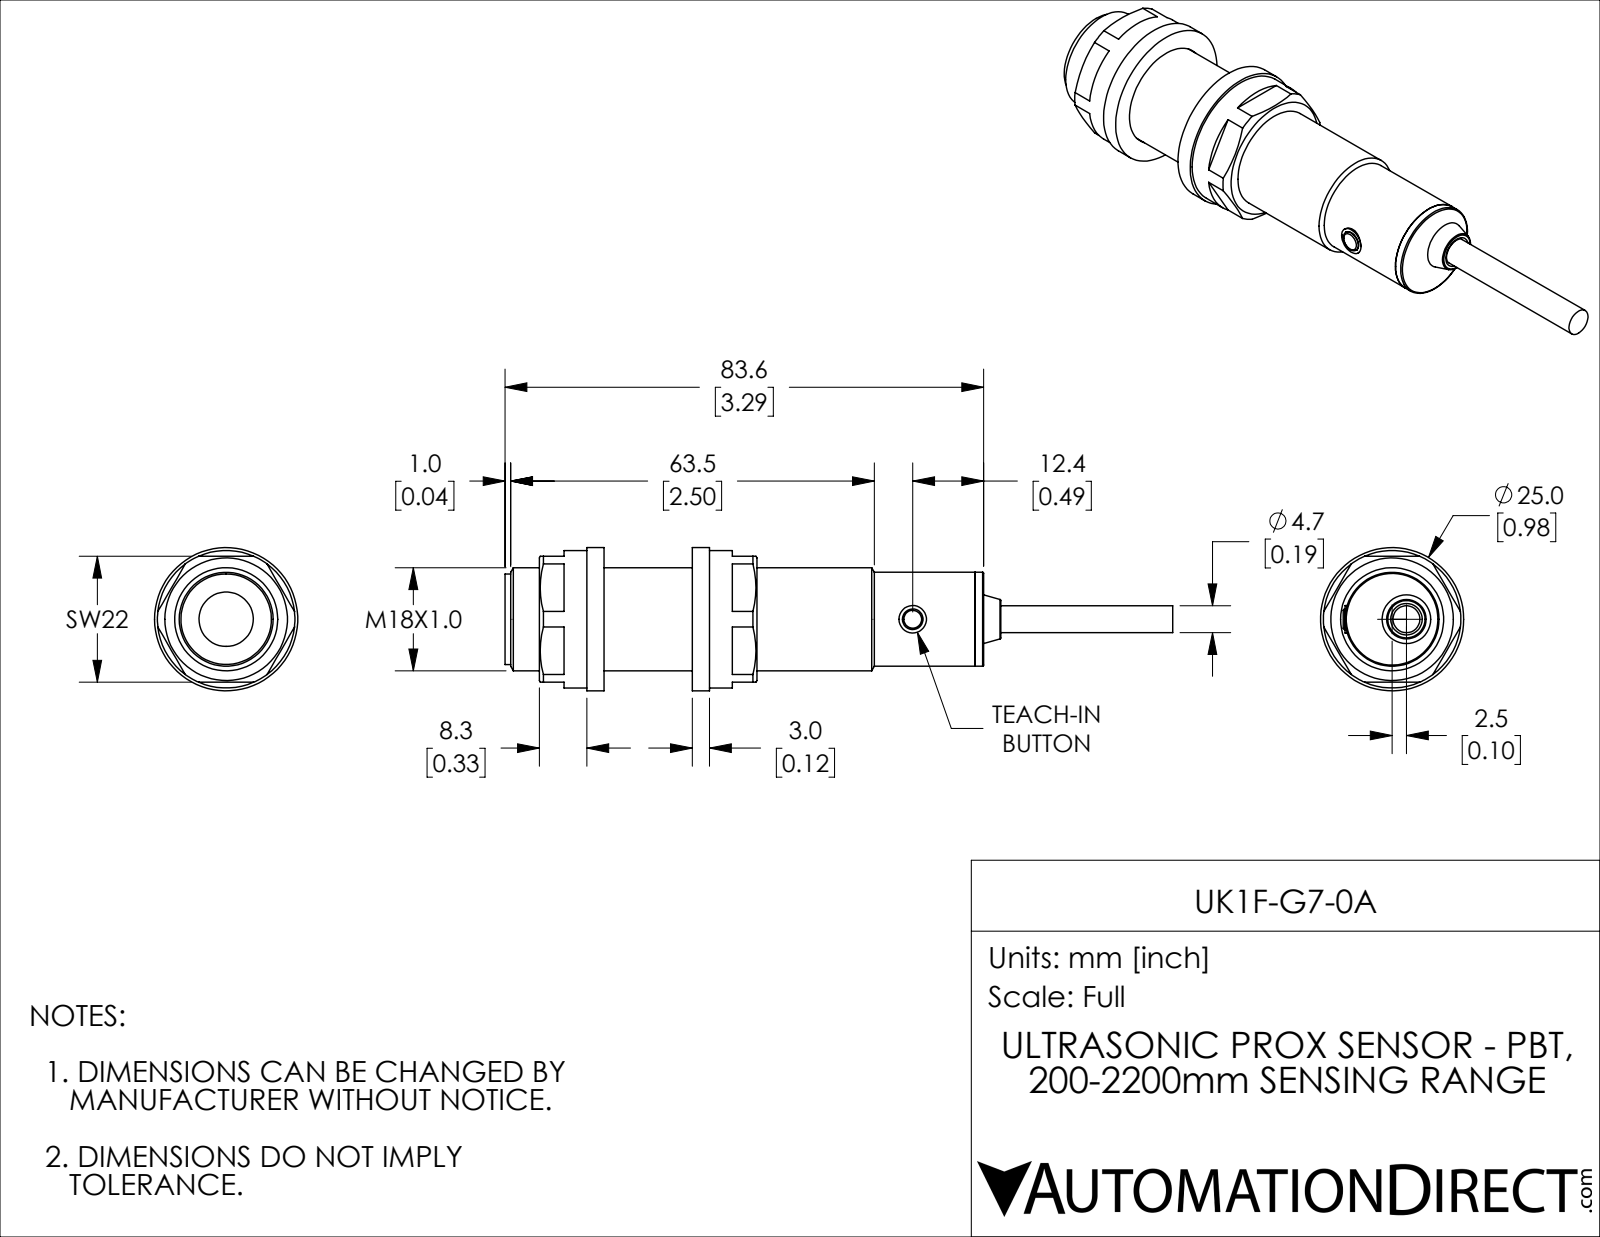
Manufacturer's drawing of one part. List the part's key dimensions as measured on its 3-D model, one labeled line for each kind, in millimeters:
Part name (STEP PRODUCT): UK1F-G7-0A
STEP written by: SolidWorks 2018 (AUTOMOTIVE_DESIGN)
Units: millimetres
Bodies: 10 solids, 107 faces (49 planar, 40 cylindrical, 18 other)
Overall size (bounding box): 116.6 × 25 × 25
Volume: 25 220 mm³ · Surface area: 11 419 mm²
Round holes (diameter × count): ⌀4.7 ×2, ⌀3.6 ×1, ⌀9.5 ×1, ⌀18 ×1, ⌀18.2 ×1
Round bosses / shafts (diameter × count): ⌀25 ×1, ⌀24 ×1, ⌀16.4 ×1, ⌀15.8 ×1, ⌀5.4 ×1, ⌀4.8 ×1
Main face-to-face distances: 3, 18.4, 21.4, 67.8, 46.4, 13.3, 34.7, 81.1, 16.3, 64.8
Hole centre spacings: 2.5
